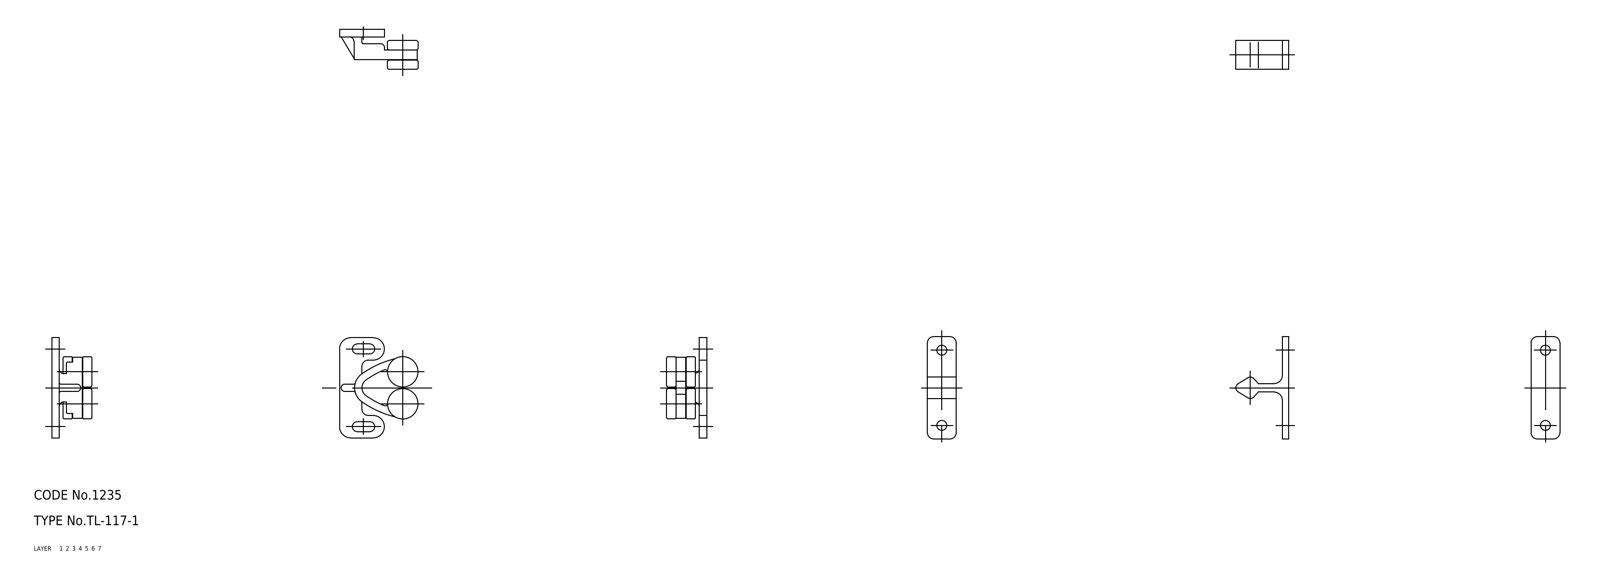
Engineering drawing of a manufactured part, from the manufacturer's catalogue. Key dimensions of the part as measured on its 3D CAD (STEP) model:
Part name (STEP PRODUCT): roller; keeper; base; TL_117_1_28778_36
STEP written by: CADfix (AUTOMOTIVE_DESIGN)
Units: millimetres
Bodies: 4 solids, 142 faces (0 planar, 0 cylindrical, 142 other)
Overall size (bounding box): 60 × 32 × 12.5
Volume: 3 165 mm³ · Surface area: 3 642 mm²
